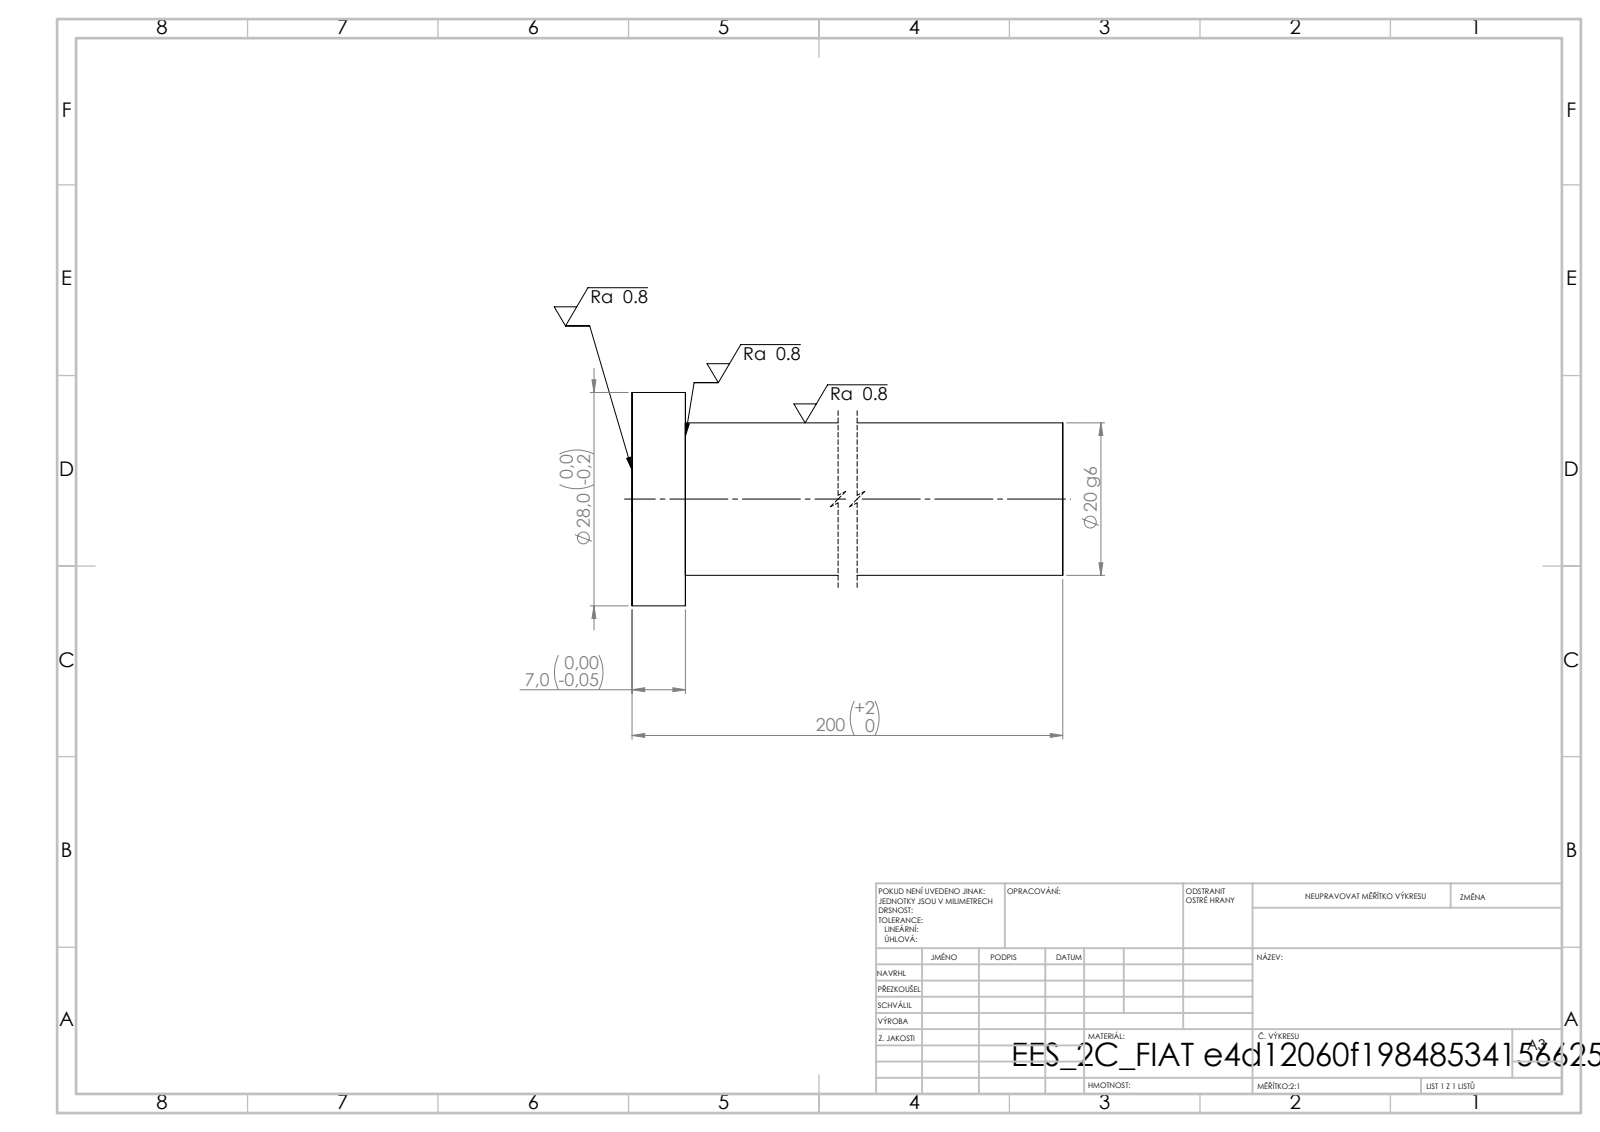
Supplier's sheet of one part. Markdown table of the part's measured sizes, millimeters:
| quantity | value |
| --- | --- |
| STEP written by | SolidWorks 2019 (CONFIG_CONTROL_DESIGN) |
| units | millimeters |
| bodies | 1 solid, 7 faces (3 planar, 4 cylindrical, 0 other) |
| overall size | 200 × 28 × 28 |
| volume | 64 943 mm³ |
| surface area | 13 974 mm² |
| round bosses / shafts (diameter × count) | 28 × 1, 20 × 1 |
| main face-to-face distances | 200, 7, 193 |
